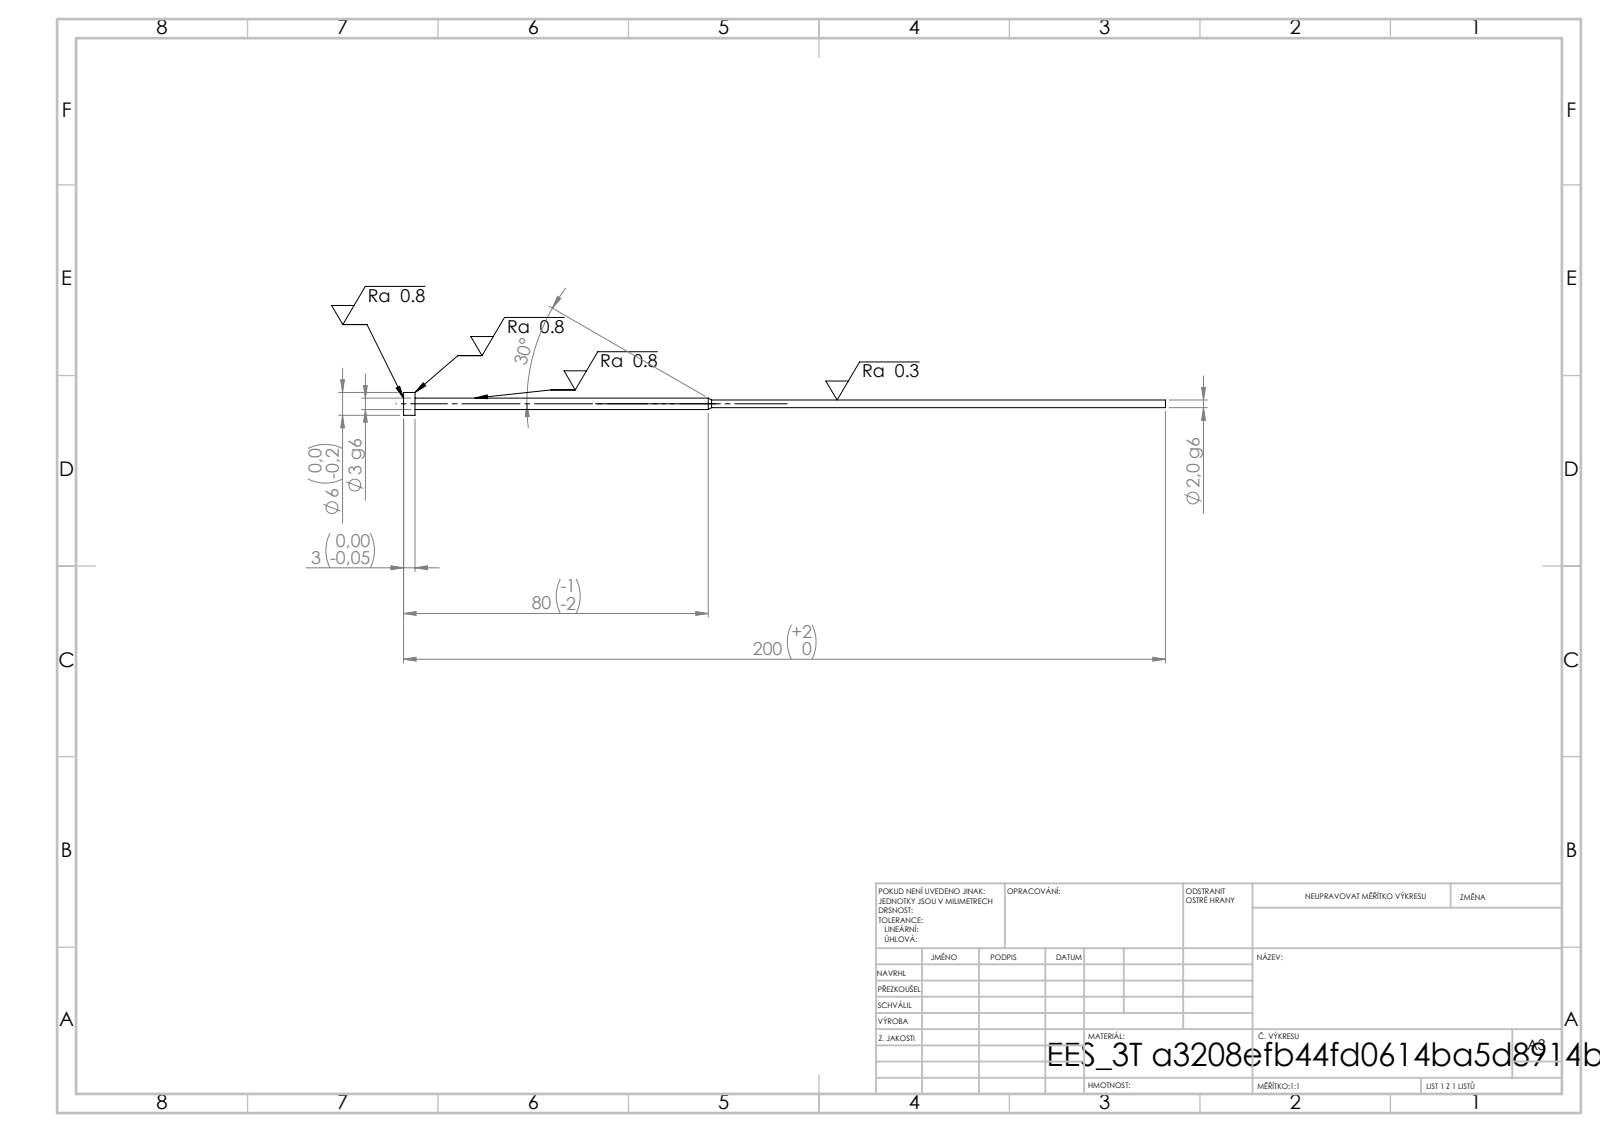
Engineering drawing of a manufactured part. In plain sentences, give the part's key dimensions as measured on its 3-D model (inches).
Its 3-D file was written by "SolidWorks 2019 (CONFIG_CONTROL_DESIGN)". It is 1 solid with 11 faces: 3 planar, 6 cylindrical and 2 other. Overall it measures 7.874 by 0.236 by 0.236 inches. Its volume is 0.062 cubic inches and its surface area 2.466 square inches. Round bosses or shafts: 1 of diameter 0.236, 1 of diameter 0.118, 1 of diameter 0.079. The main face-to-face distances are 0.118, 7.756, 7.874.
